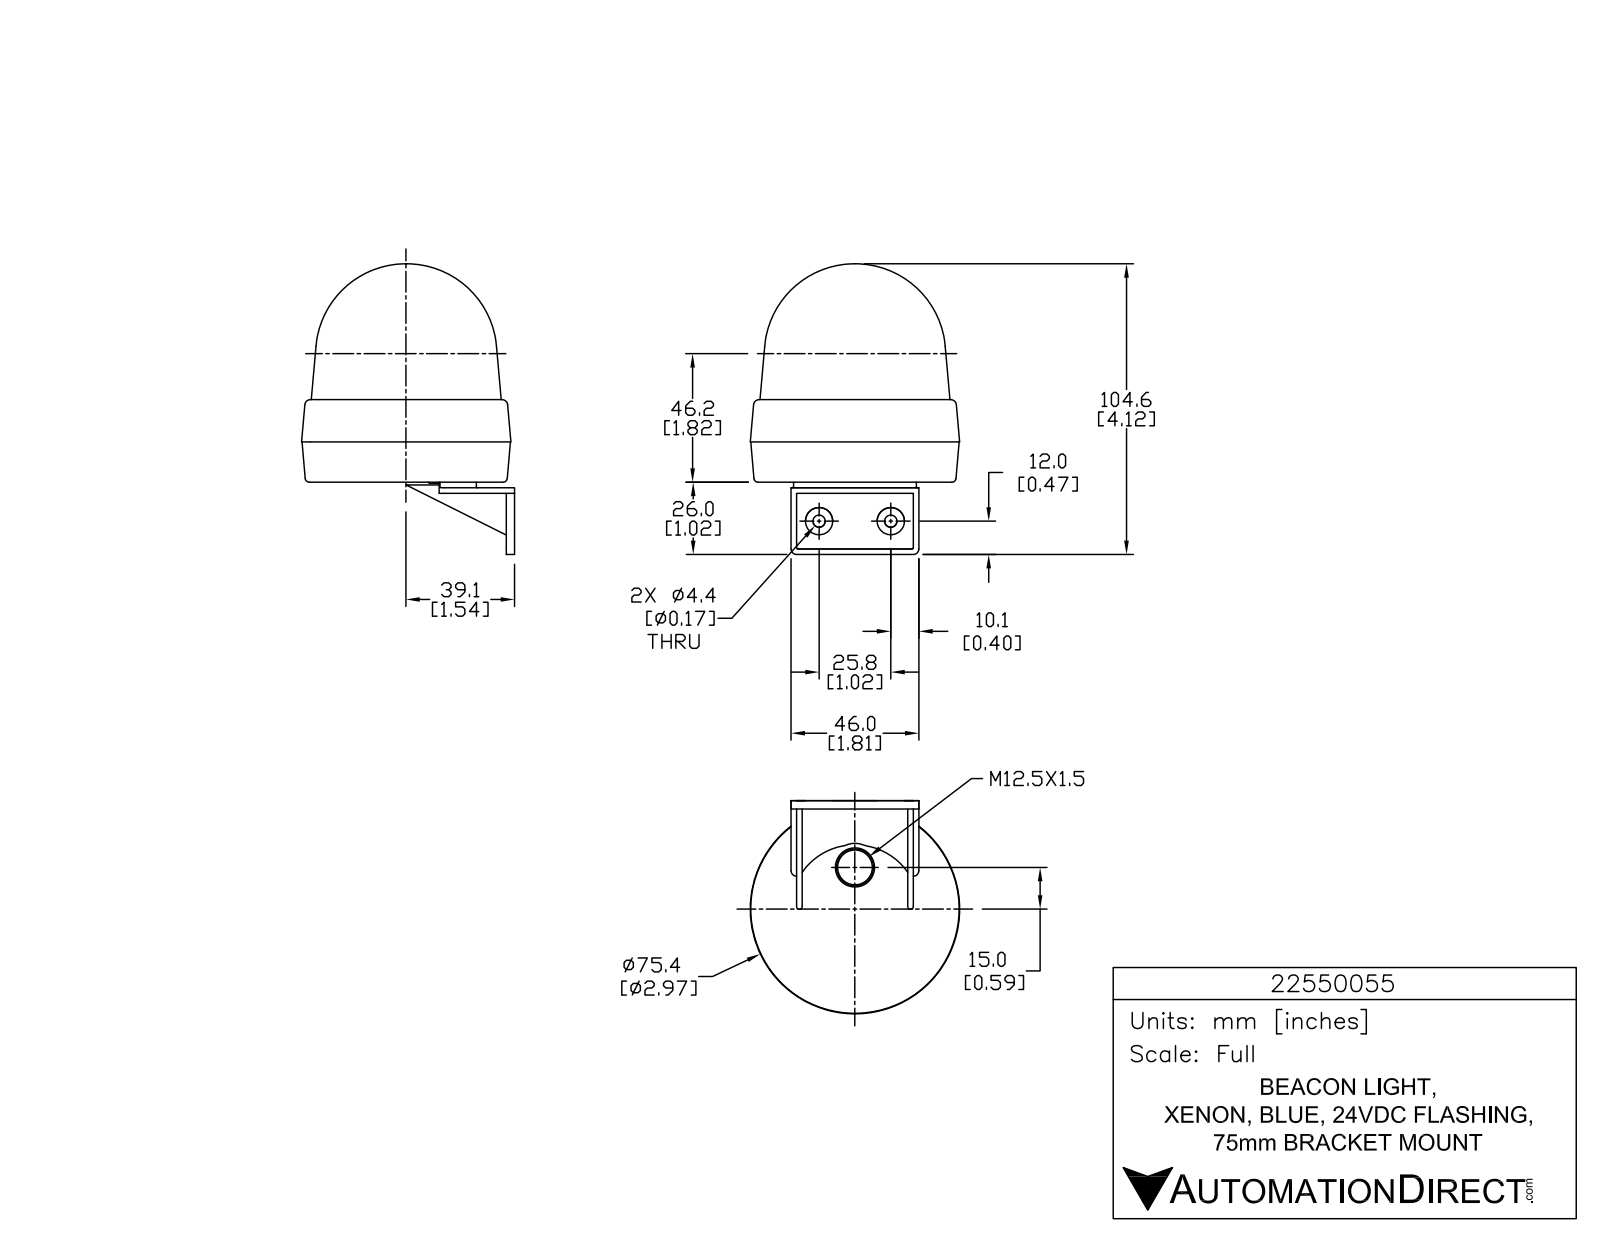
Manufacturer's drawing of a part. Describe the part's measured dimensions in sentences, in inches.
The part is named "22550055". Its 3-D file was written by "SolidWorks 2015 (AUTOMOTIVE_DESIGN)". It is 1 solid with 819 faces: 549 planar, 180 cylindrical and 90 other. Overall it measures 4.117 by 3.253 by 2.967 inches. Its volume is 16.02 cubic inches and its surface area 41.97 square inches. Round holes: 3 of diameter 0.059, 2 of diameter 0.173. Round bosses or shafts: 3 of diameter 0.339, 3 of diameter 0.084, 2 of diameter 0.386. Partial cylindrical surfaces (rounded edges, fillets, slot ends): 9 of radius 0.005, 6 of radius 0.005, 6 of radius 0.012, 6 of radius 0.012, 6 of radius 0.012, 6 of radius 0.02, 6 of radius 0.196, 4 of radius 0.079. The main face-to-face distances are 0.079, 0.157, 1.574, 0.039, 0.118, 1.653, 1.496, 0.079, 1.654, 1.732. The hole center spacings are 1.016.
